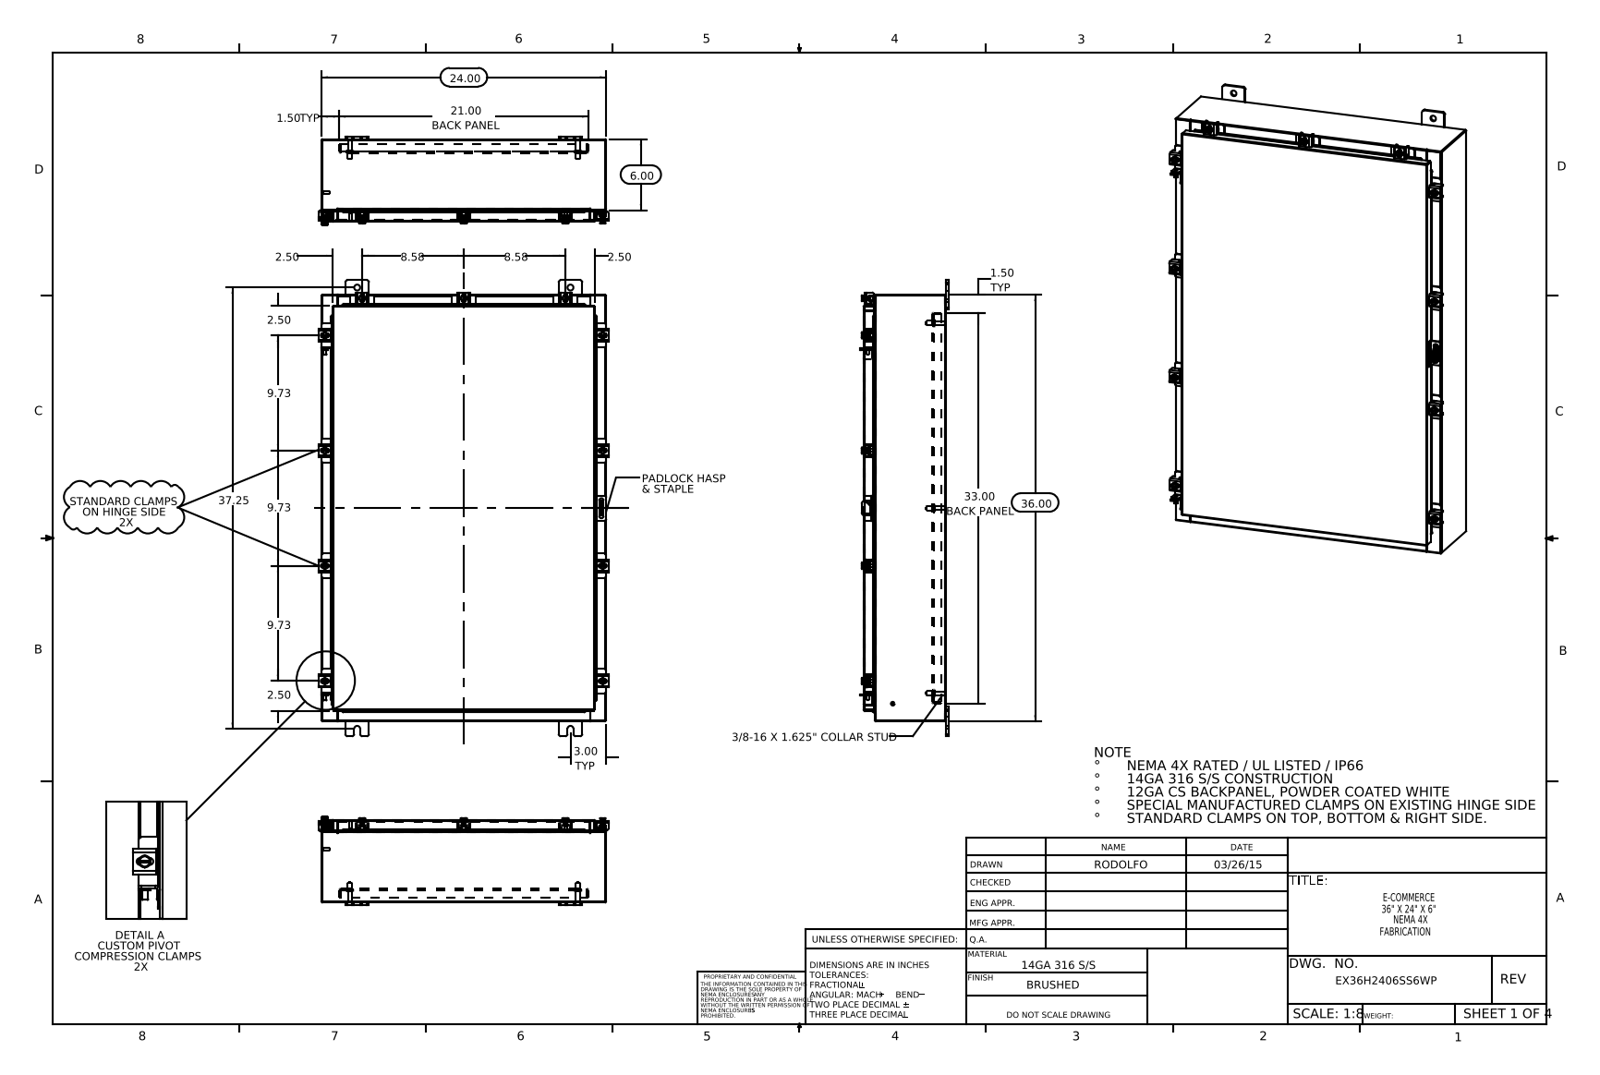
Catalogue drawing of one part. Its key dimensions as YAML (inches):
part_name: "22101002_RTP29; EX36H2406SS6WP Body; N-WMT04X30402202210-00 22104005_DEFAULT; EX36H2406SS6WP Top (+8 more)"
step_written_by: "SolidWorks 2014 (CONFIG_CONTROL_DESIGN)"
units: inches
bodies: {solids: 78, faces: 1971, planar: 1041, cylindrical: 758, other: 172}
overall_size: [38.5, 24.421, 7.453]
volume: 290.3
surface_area: 7154
round_holes:
  - {diameter: 0.213, count: 11}
  - {diameter: 0.26, count: 11}
  - {diameter: 0.5, count: 10}
  - {diameter: 0.125, count: 1}
  - {diameter: 0.25, count: 1}
round_bosses_or_shafts:
  - {diameter: 0.5, count: 11}
  - {diameter: 0.25, count: 11}
  - {diameter: 0.399, count: 9}
  - {diameter: 0.625, count: 6}
  - {diameter: 0.375, count: 6}
  - {diameter: 0.33, count: 6}
  - {diameter: 0.315, count: 2}
  - {diameter: 0.236, count: 2}
partial_cylinders:
  - {radius: 0.06, count: 48}
  - {radius: 0.013, count: 26}
  - {radius: 0.19, count: 24}
  - {radius: 0.088, count: 22}
  - {radius: 0.141, count: 22}
  - {radius: 0.09, count: 20}
  - {radius: 0.12, count: 20}
  - {radius: 0.05, count: 19}
face_to_face_distances: [0.075, 6.9, 6.975, 6.826, 0.104, 1, 1.075, 5.826, 5.9, 1.179]
hole_center_spacings: [25.389, 5.299, 9.73, 10.964, 14.744, 15.625, 19.459, 20.597]
